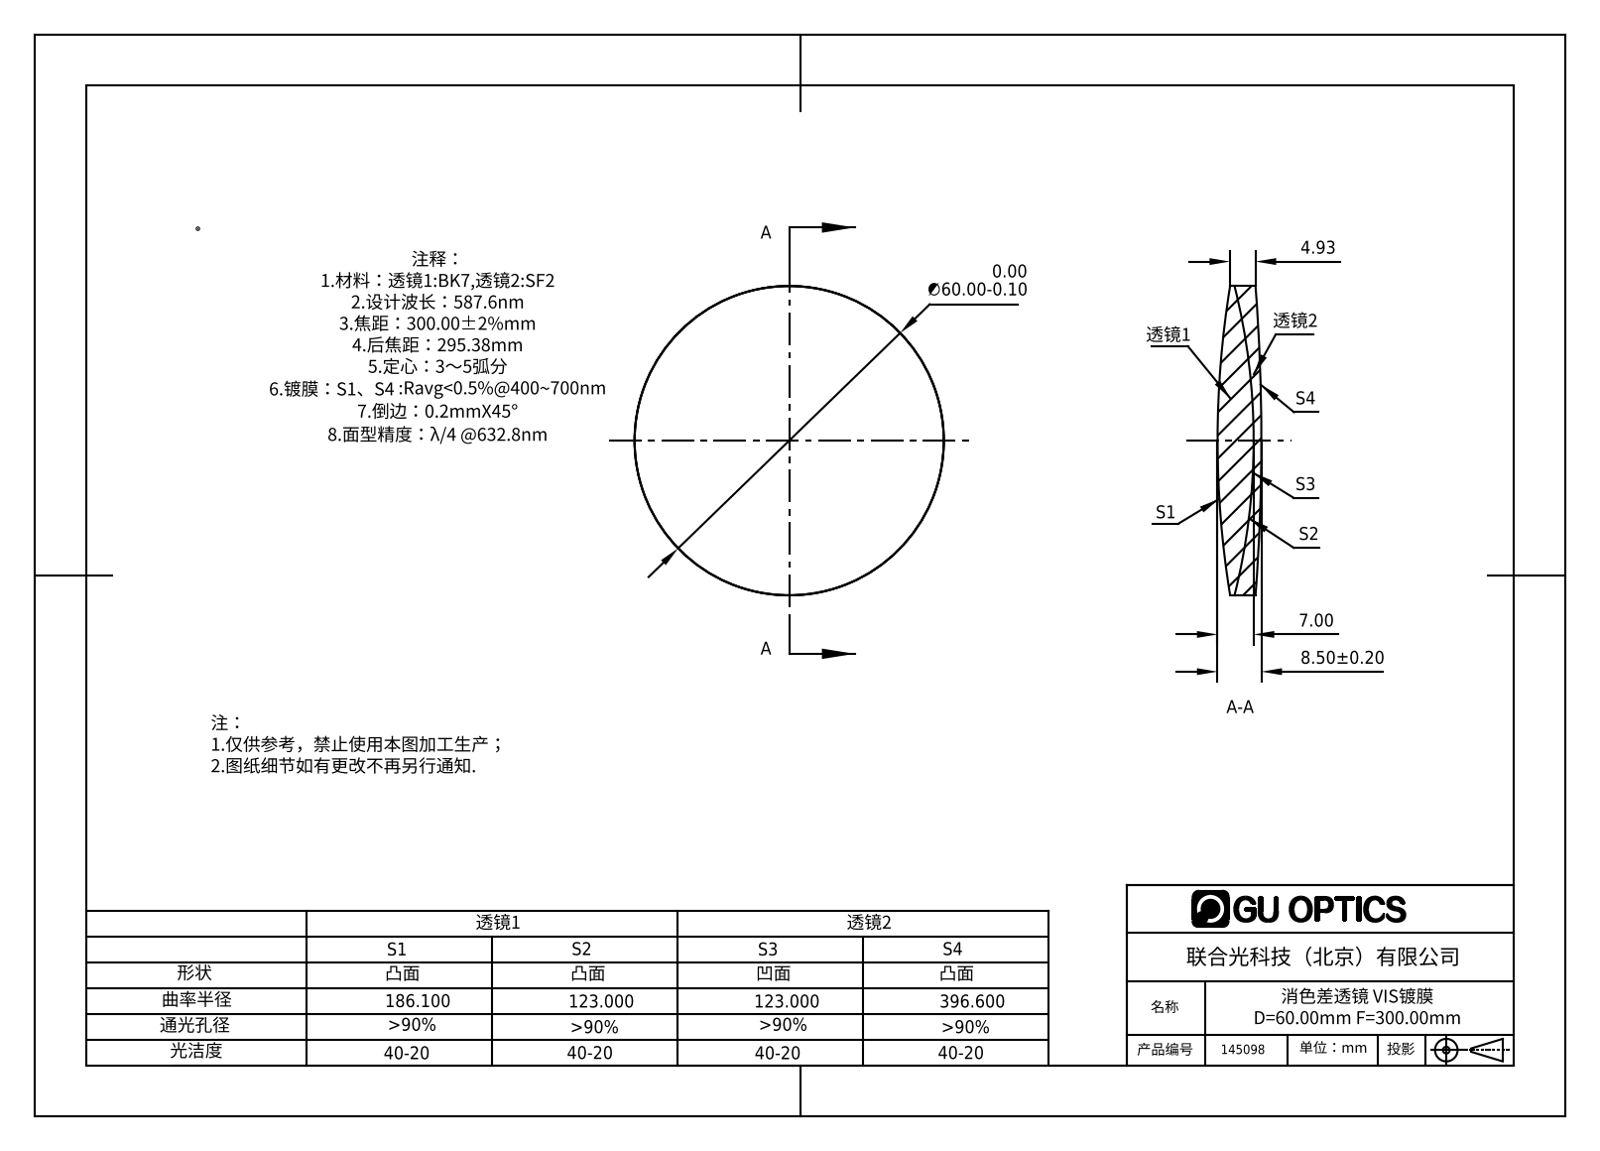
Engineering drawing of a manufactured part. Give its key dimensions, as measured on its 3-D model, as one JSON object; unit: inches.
{"part_name": "145098", "step_written_by": "SolidWorks 2016 (AUTOMOTIVE_DESIGN)", "units": "inches", "bodies": {"solids": 2, "faces": 12, "planar": 0, "cylindrical": 4, "other": 8}, "overall_size": [2.362, 2.362, 0.335], "volume_in3": 1.159, "surface_area_in2": 19.14, "round_bosses_or_shafts": [[2.362, 1]]}
